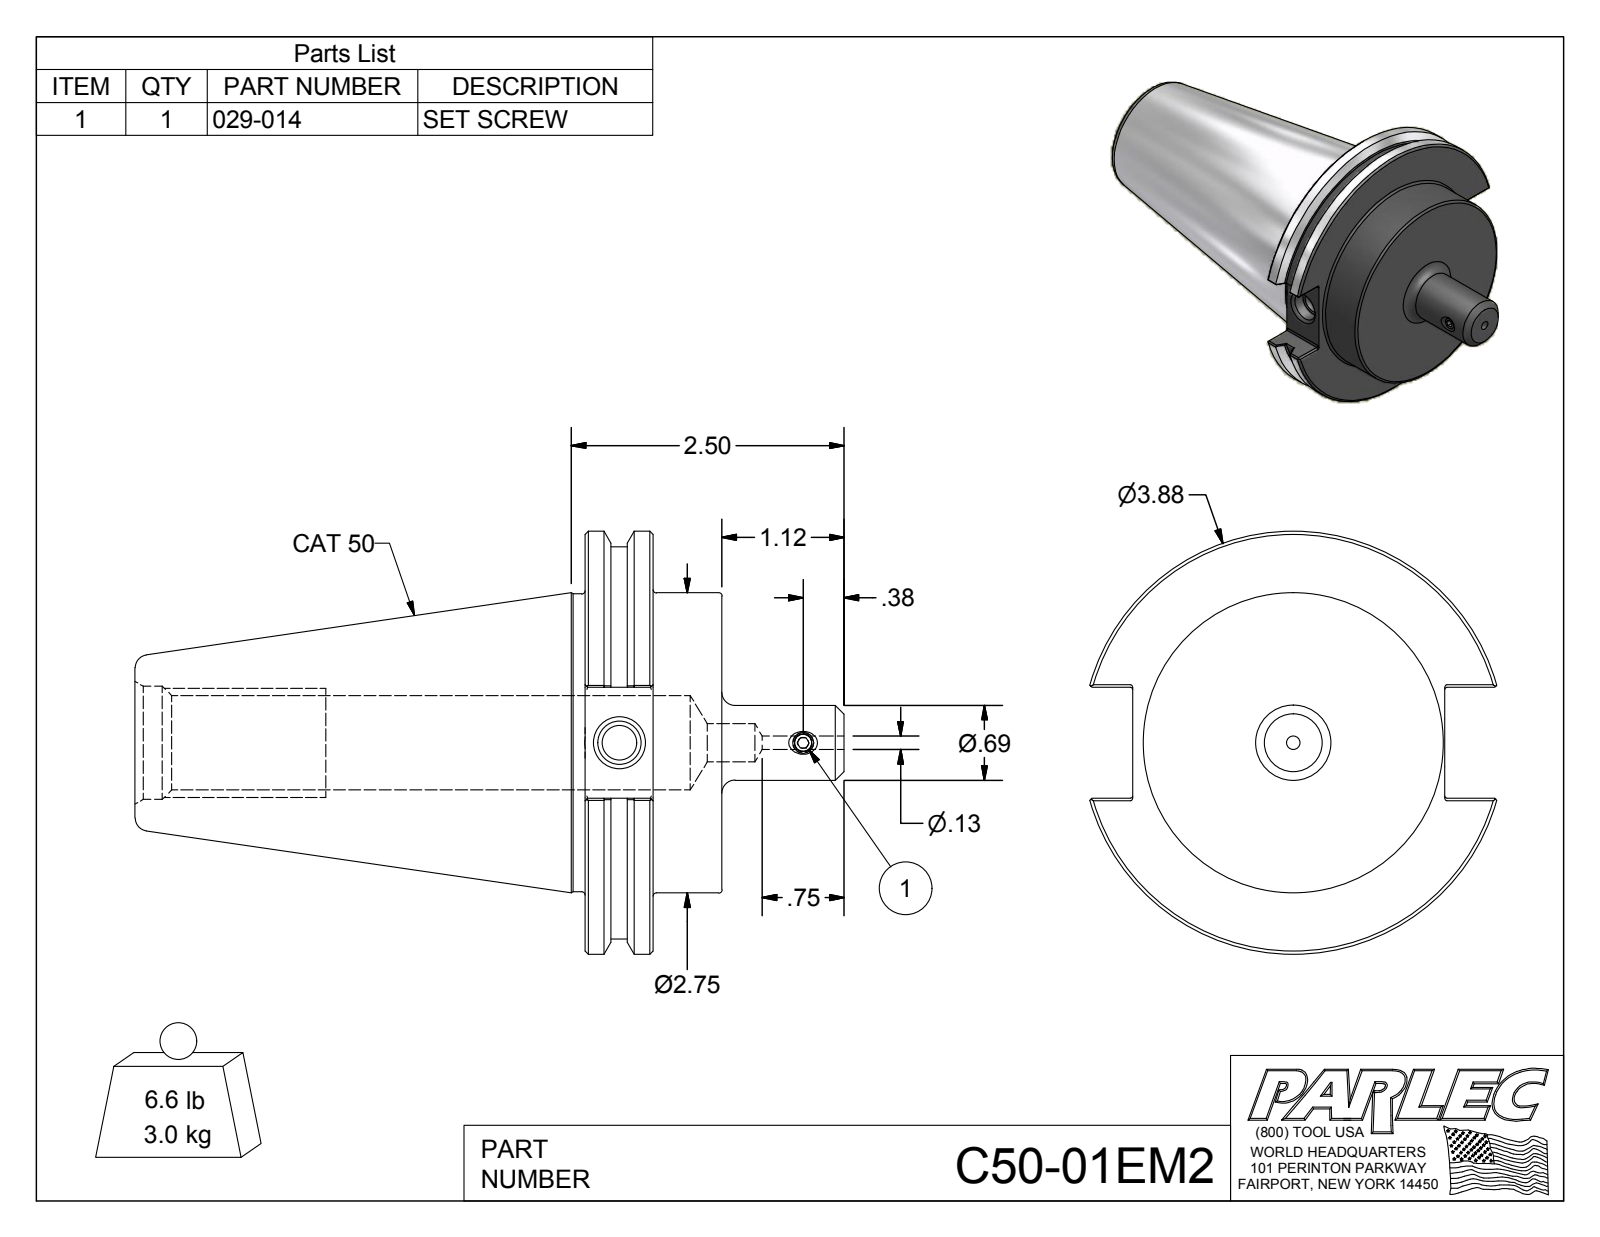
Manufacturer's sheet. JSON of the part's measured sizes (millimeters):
{"part_name": "C50-01EM2; C50-01EM2-1; 029-014", "step_written_by": "Autodesk Inventor 2012 (AUTOMOTIVE_DESIGN)", "units": "millimeters", "bodies": {"solids": 2, "faces": 105, "planar": 41, "cylindrical": 30, "other": 34}, "overall_size": [165.1, 98.4, 94.7], "volume_mm3": 380500, "surface_area_mm2": 50810, "round_holes": [[3.2, 1], [4, 1], [8, 1], [8.9, 1], [10.1, 1], [22, 1], [26.4, 1]], "round_bosses_or_shafts": [[98.4, 1], [91.3, 1], [69.9, 1], [69.3, 1], [17.4, 1], [4.8, 1]], "partial_cylinders_radius": [[0.5, 12]], "face_to_face_distances": [31.9, 15.9, 16, 104.8, 120.7, 136.7, 72.6, 25.8, 110.8, 6], "hole_center_spacings": [42.8]}
